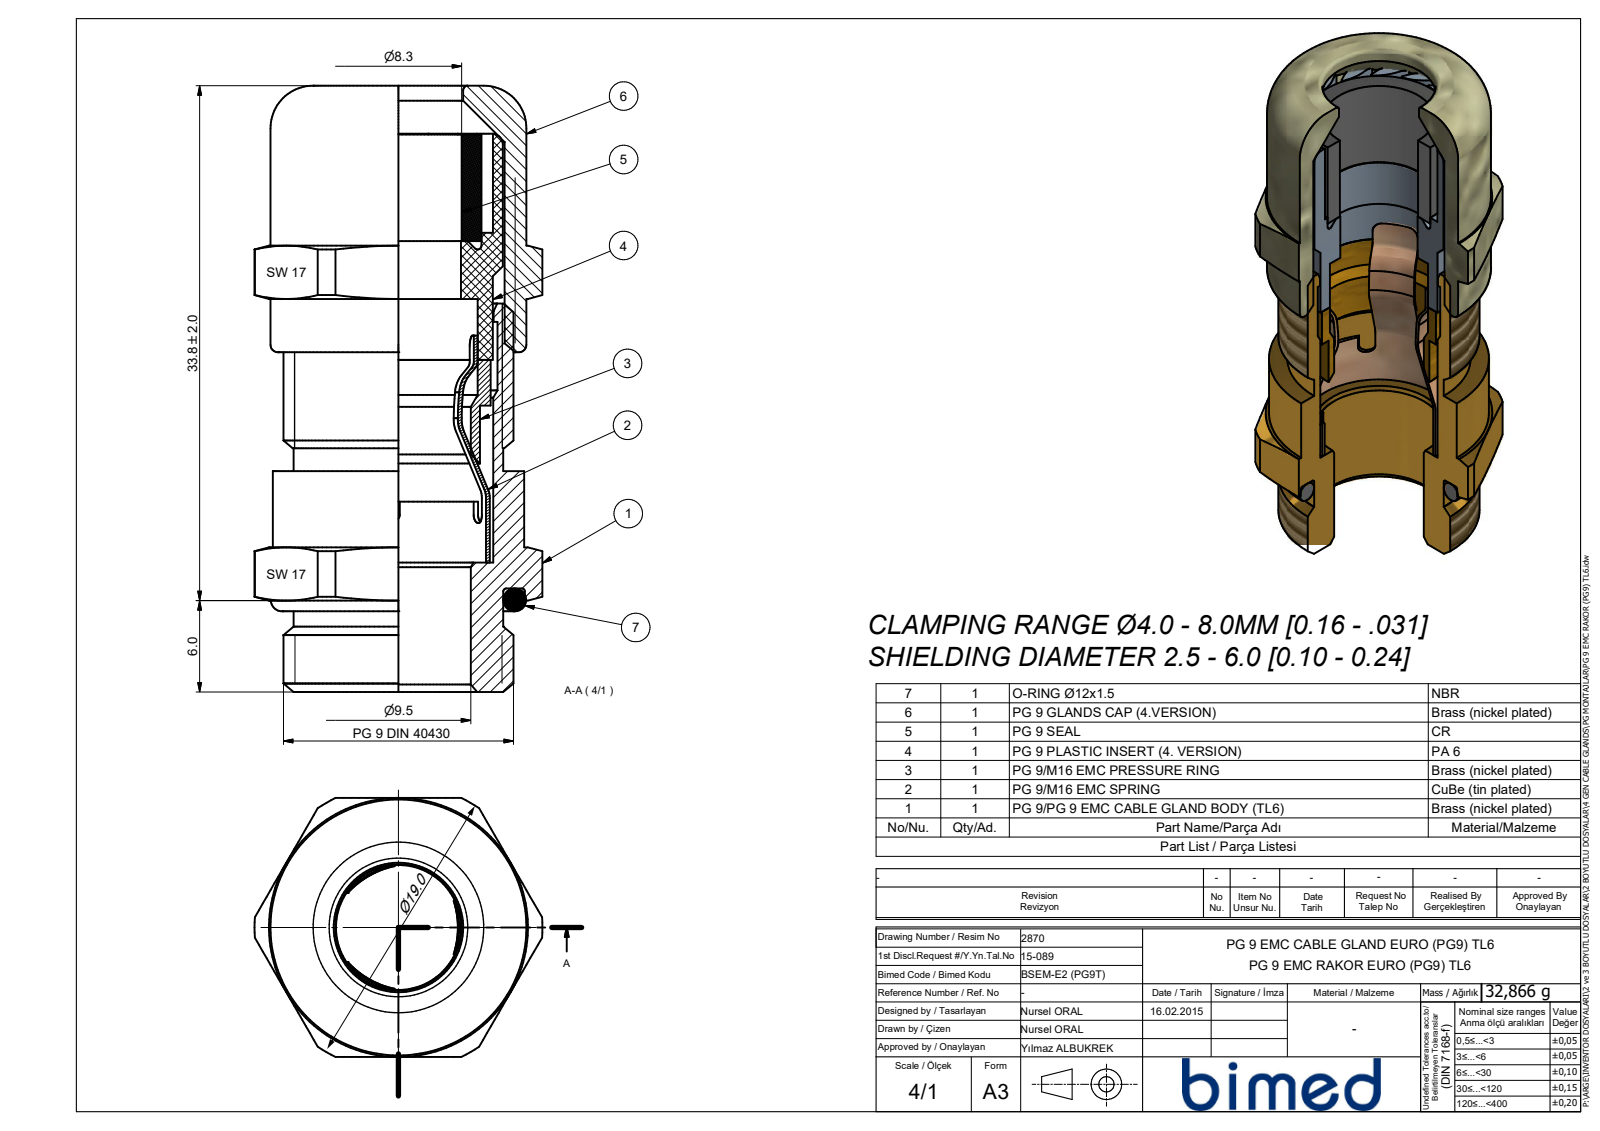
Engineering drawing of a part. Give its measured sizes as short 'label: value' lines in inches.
name: BSEM-E2-PG9T-WCL
written by: SolidWorks 2021 (CONFIG_CONTROL_DESIGN)
unit: in
bodies: 1 solid, 91 faces (23 planar, 28 cylindrical, 40 other)
size: 1.567 × 0.744 × 0.669
volume: 0.501 in³; area: 4.165 in²
bosses: 1× ⌀0.661, 1× ⌀0.65, 1× ⌀0.594, 1× ⌀0.542
rounds: 1× R0.372
face distances: 0.669, 1.567, 0.571, 0.996, 0.138, 0.878, 0.307, 0.689, 0.374, 0.197
